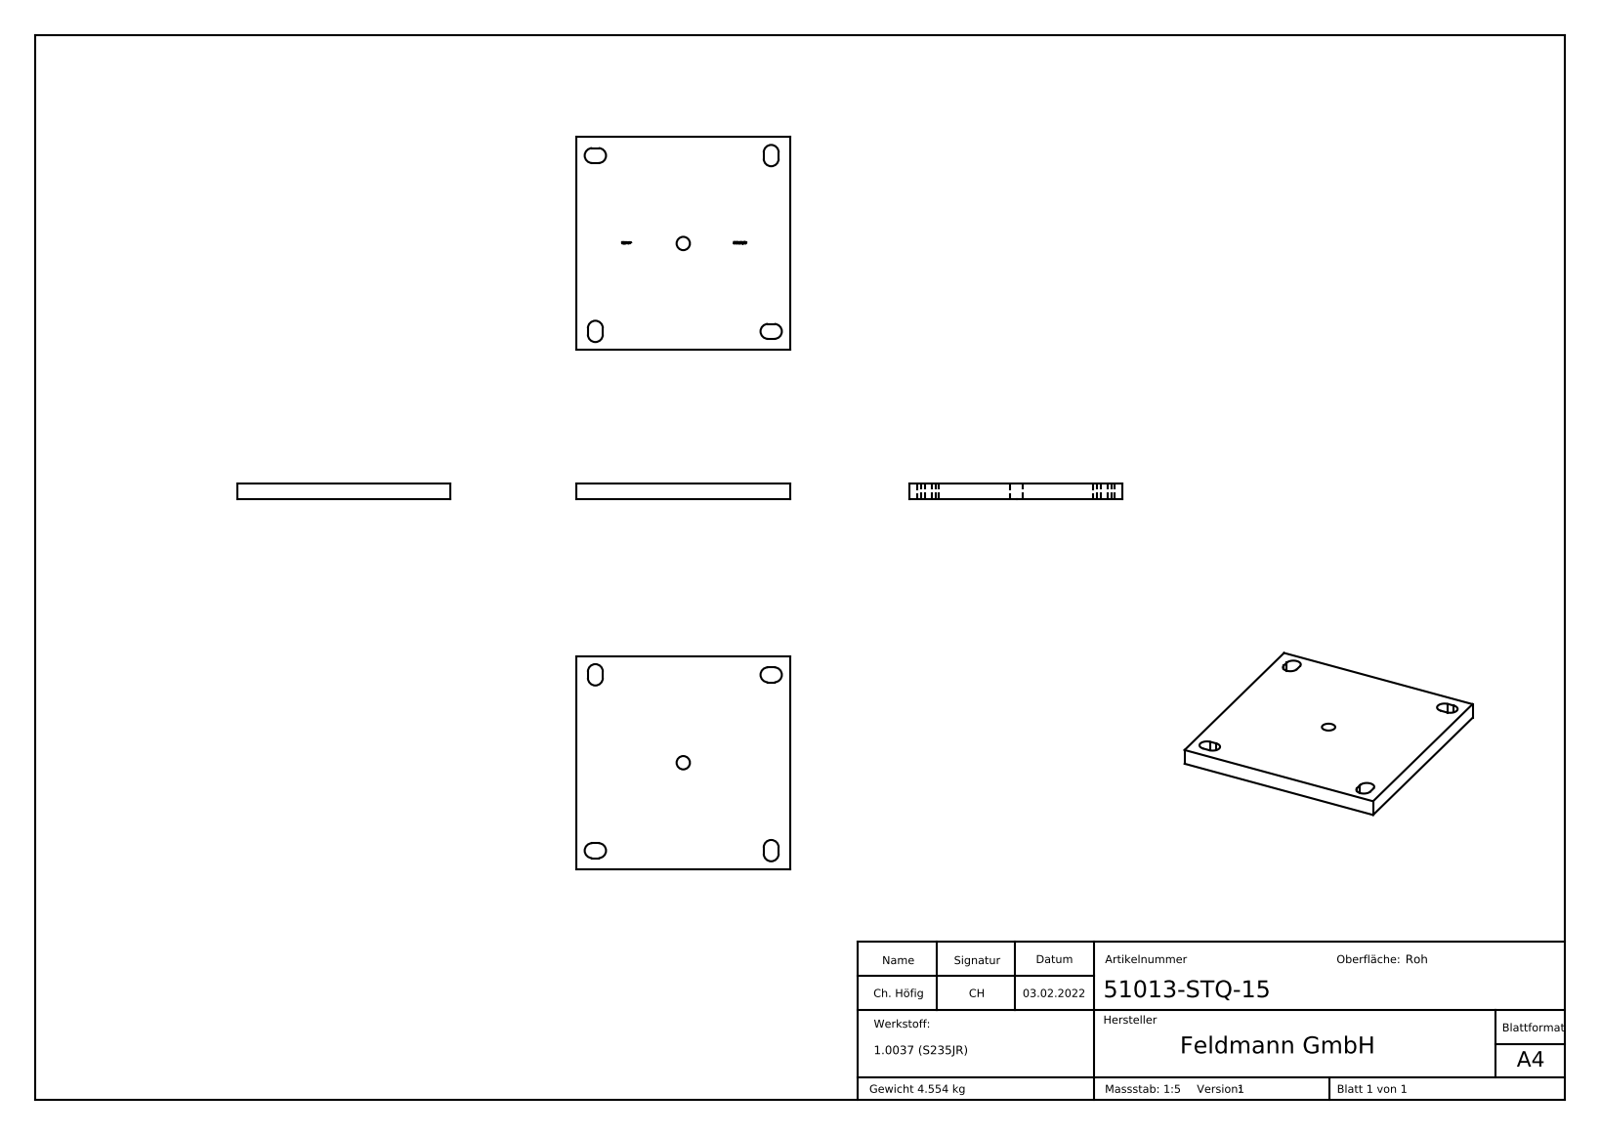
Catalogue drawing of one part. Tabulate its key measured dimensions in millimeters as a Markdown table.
| quantity | value |
| --- | --- |
| part name | 51013-STQ-15 |
| STEP written by | SolidWorks 2018 (CONFIG_CONTROL_DESIGN) |
| units | millimeters |
| bodies | 1 solid, 274 faces (150 planar, 12 cylindrical, 112 other) |
| overall size | 200 × 200 × 15 |
| volume | 583 882 mm³ |
| surface area | 93 809 mm² |
| round holes (diameter × count) | 12.5 × 1 |
| partial cylindrical surfaces (radius × count) | 7 × 8 |
| main face-to-face distances | 15, 200, 10.5, 24.5, 175.5, 189.5, 14, 165, 179, 151 |
